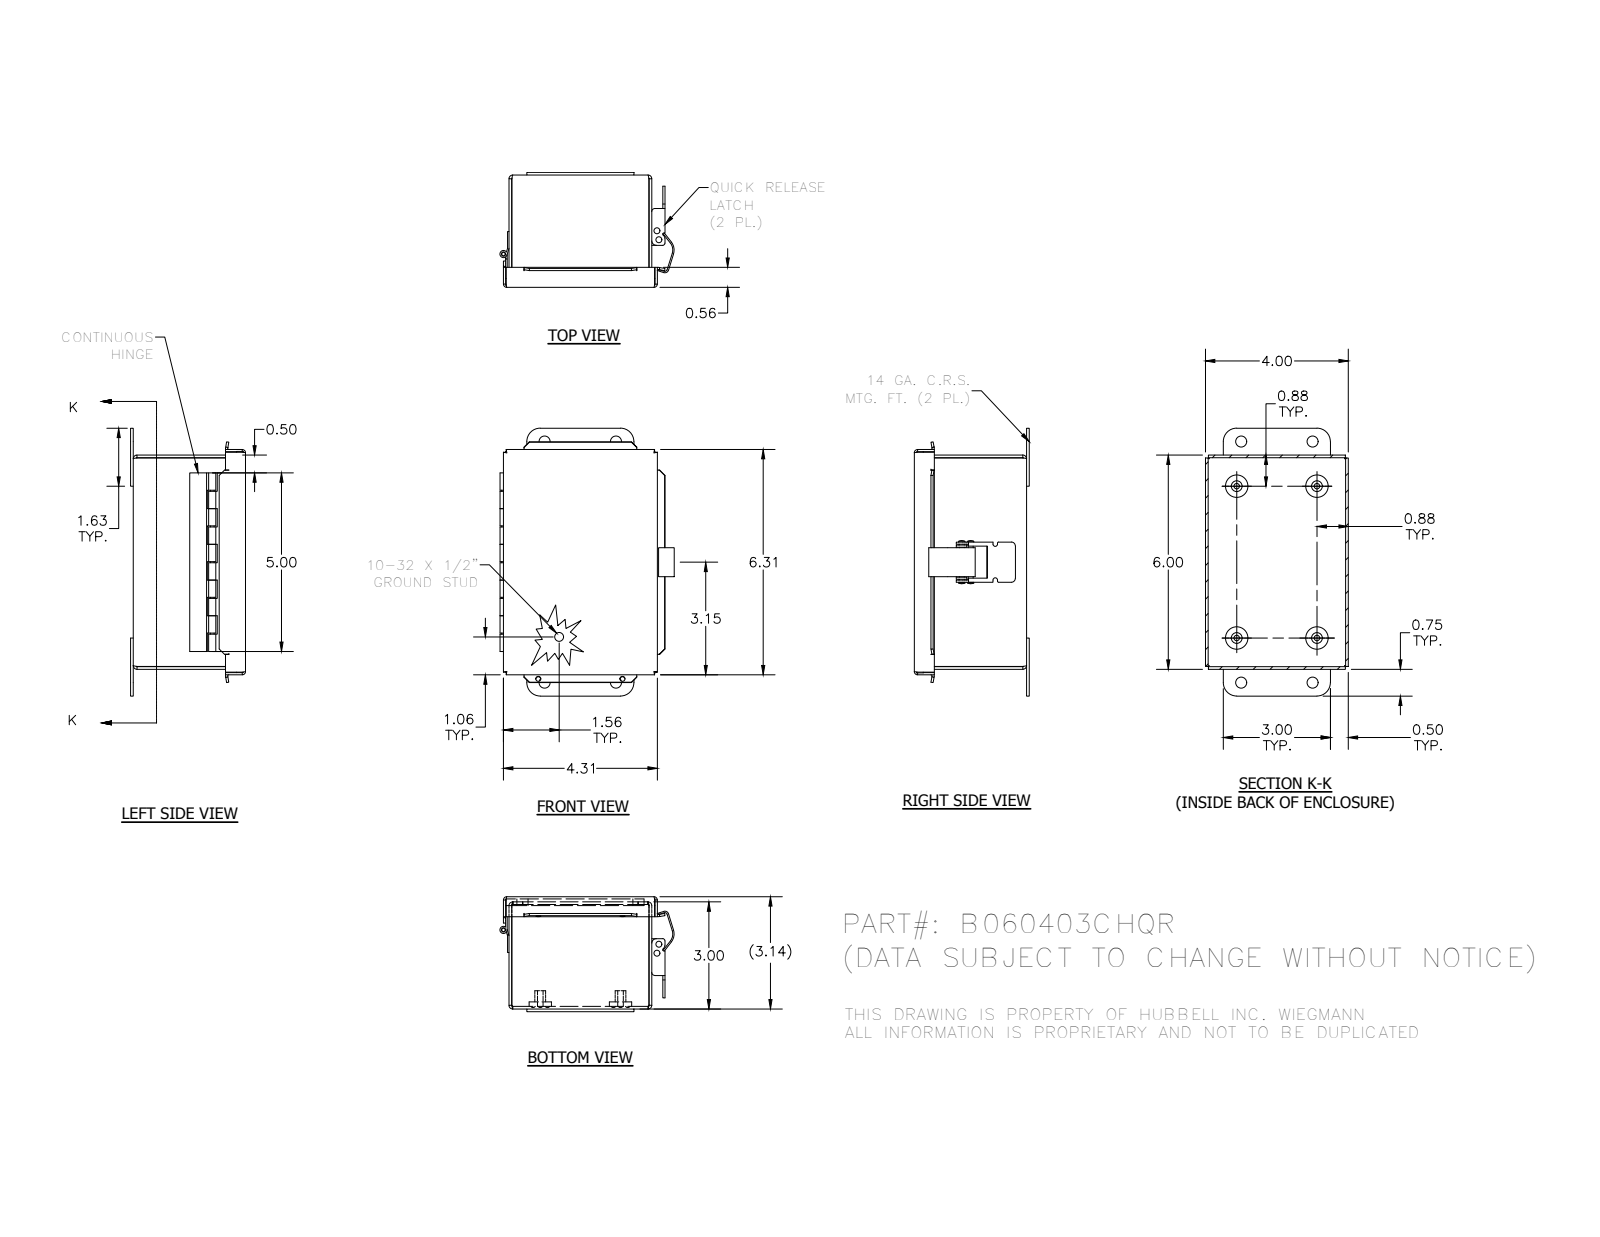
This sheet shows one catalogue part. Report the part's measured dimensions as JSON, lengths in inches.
{"part_name": "B060403CHQR; 3499; 3481; B060403CHQRBKP (+8 more)", "step_written_by": "Autodesk Inventor 2012 (AUTOMOTIVE_DESIGN)", "units": "inches", "bodies": {"solids": 19, "faces": 431, "planar": 273, "cylindrical": 115, "other": 43}, "overall_size": [7.5, 4.88, 3.219], "volume_in3": 12.49, "surface_area_in2": 342.5, "round_holes": [[0.156, 4], [0.31, 4], [0.14, 2], [0.155, 2], [0.116, 1], [0.17, 1]], "round_bosses_or_shafts": [[0.625, 4], [0.3, 4], [0.25, 2], [0.169, 2], [0.136, 2], [0.2, 1], [0.19, 1], [0.1, 1]], "partial_cylinders_radius": [[0.031, 18], [0.105, 8], [0.093, 7], [0.375, 4], [0.063, 3], [0.109, 2], [0.125, 2], [0.062, 1]], "face_to_face_distances": [0.074, 3.926, 3.083, 3.144, 0.062, 3.009, 3.07, 5.926, 4, 3.852], "hole_center_spacings": [1.256, 5.502, 2, 2.25, 2.465, 2.466, 5.897, 6.75]}
